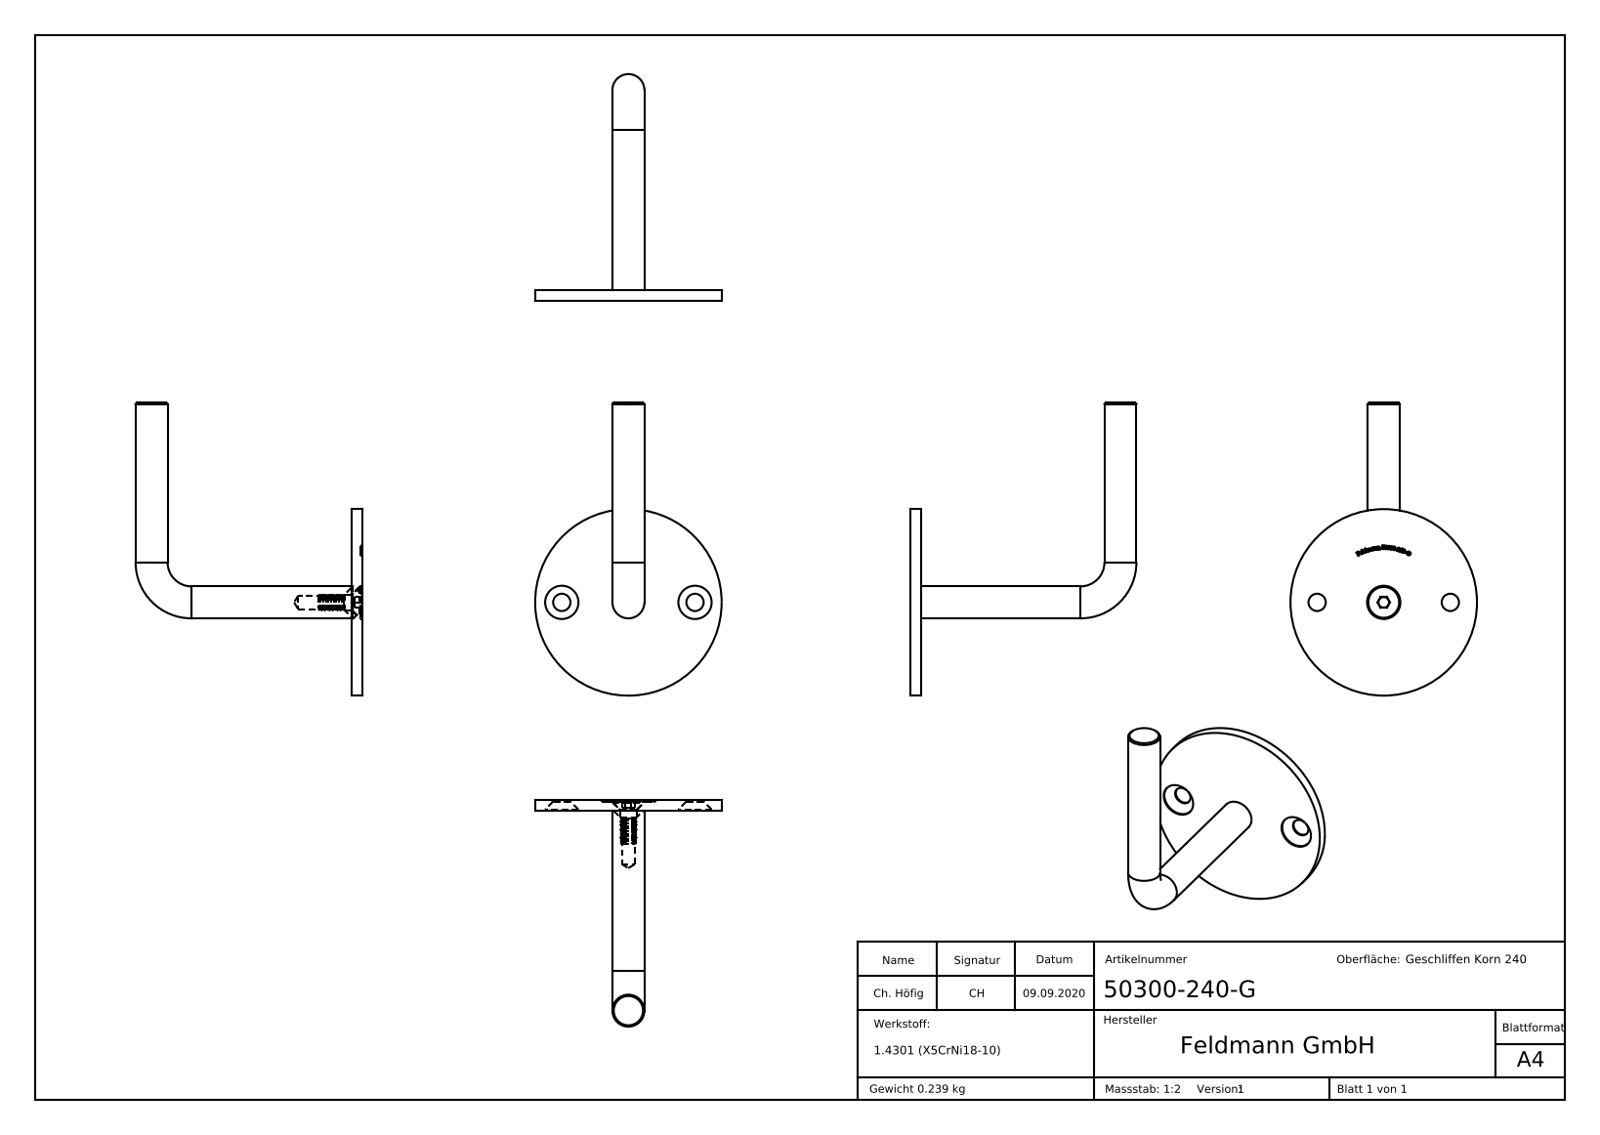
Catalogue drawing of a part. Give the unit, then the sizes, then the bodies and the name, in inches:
Units: inches
Overall size (bounding box): 4.331 × 3.346 × 2.756
Round holes (diameter × count): ⌀0.256 ×3, ⌀0.492 ×3, ⌀0.197 ×1
Round bosses / shafts (diameter × count): ⌀0.472 ×2, ⌀2.756 ×1, ⌀0.456 ×1, ⌀0.236 ×1
Main face-to-face distances: 0.157, 0.018, 0.14, 0.648, 0.63, 0.49, 0.158, 0.02, 0.138, 0.628
Hole centre spacings: 0.984, 1.969
Volume: 1.876 in³ · Surface area: 23.52 in²
Bodies: 3 solids, 366 faces (139 planar, 44 cylindrical, 183 other)
Part name (STEP PRODUCT): socket countersunk head screw_din; 50300-240-G Teil1; 50300-240-G Teil2; 50300-240-G Teil2_50300-240-G Teil2 (+3 more)
STEP written by: SolidWorks 2018 (CONFIG_CONTROL_DESIGN)
